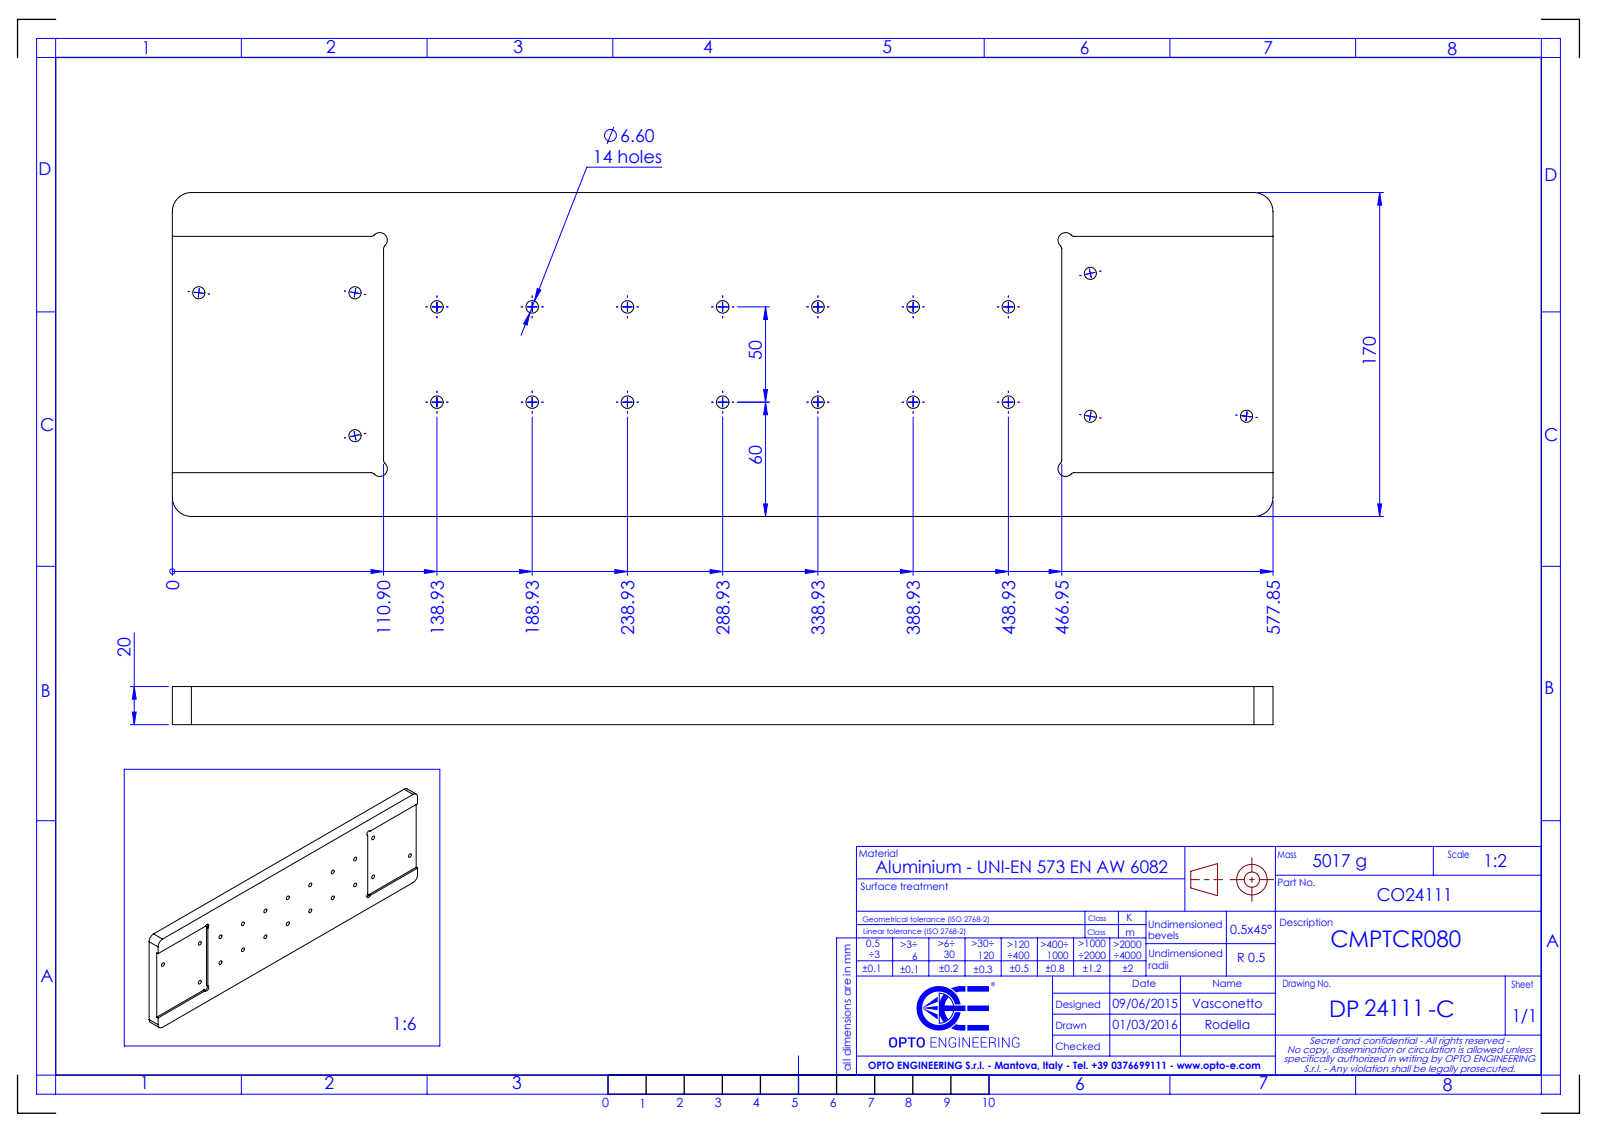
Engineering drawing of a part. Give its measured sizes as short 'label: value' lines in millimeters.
name: DP24111
written by: SolidWorks 2021 (CONFIG_CONTROL_DESIGN)
unit: mm
bodies: 1 solid, 90 faces (20 planar, 70 cylindrical, 0 other)
size: 577.85 × 170 × 20
volume: 1 865 000 mm³; area: 234 307 mm²
holes: 14× ⌀6.6, 6× ⌀6.4, 6× ⌀11
rounds: 8× R2, 4× R4, 4× R10
face distances: 20, 17, 3, 170, 577.85, 23, 147, 110.9, 466.95, 124
hole spacings: 50, 70.71, 100, 111.8, 150, 158.11, 200, 206.16
